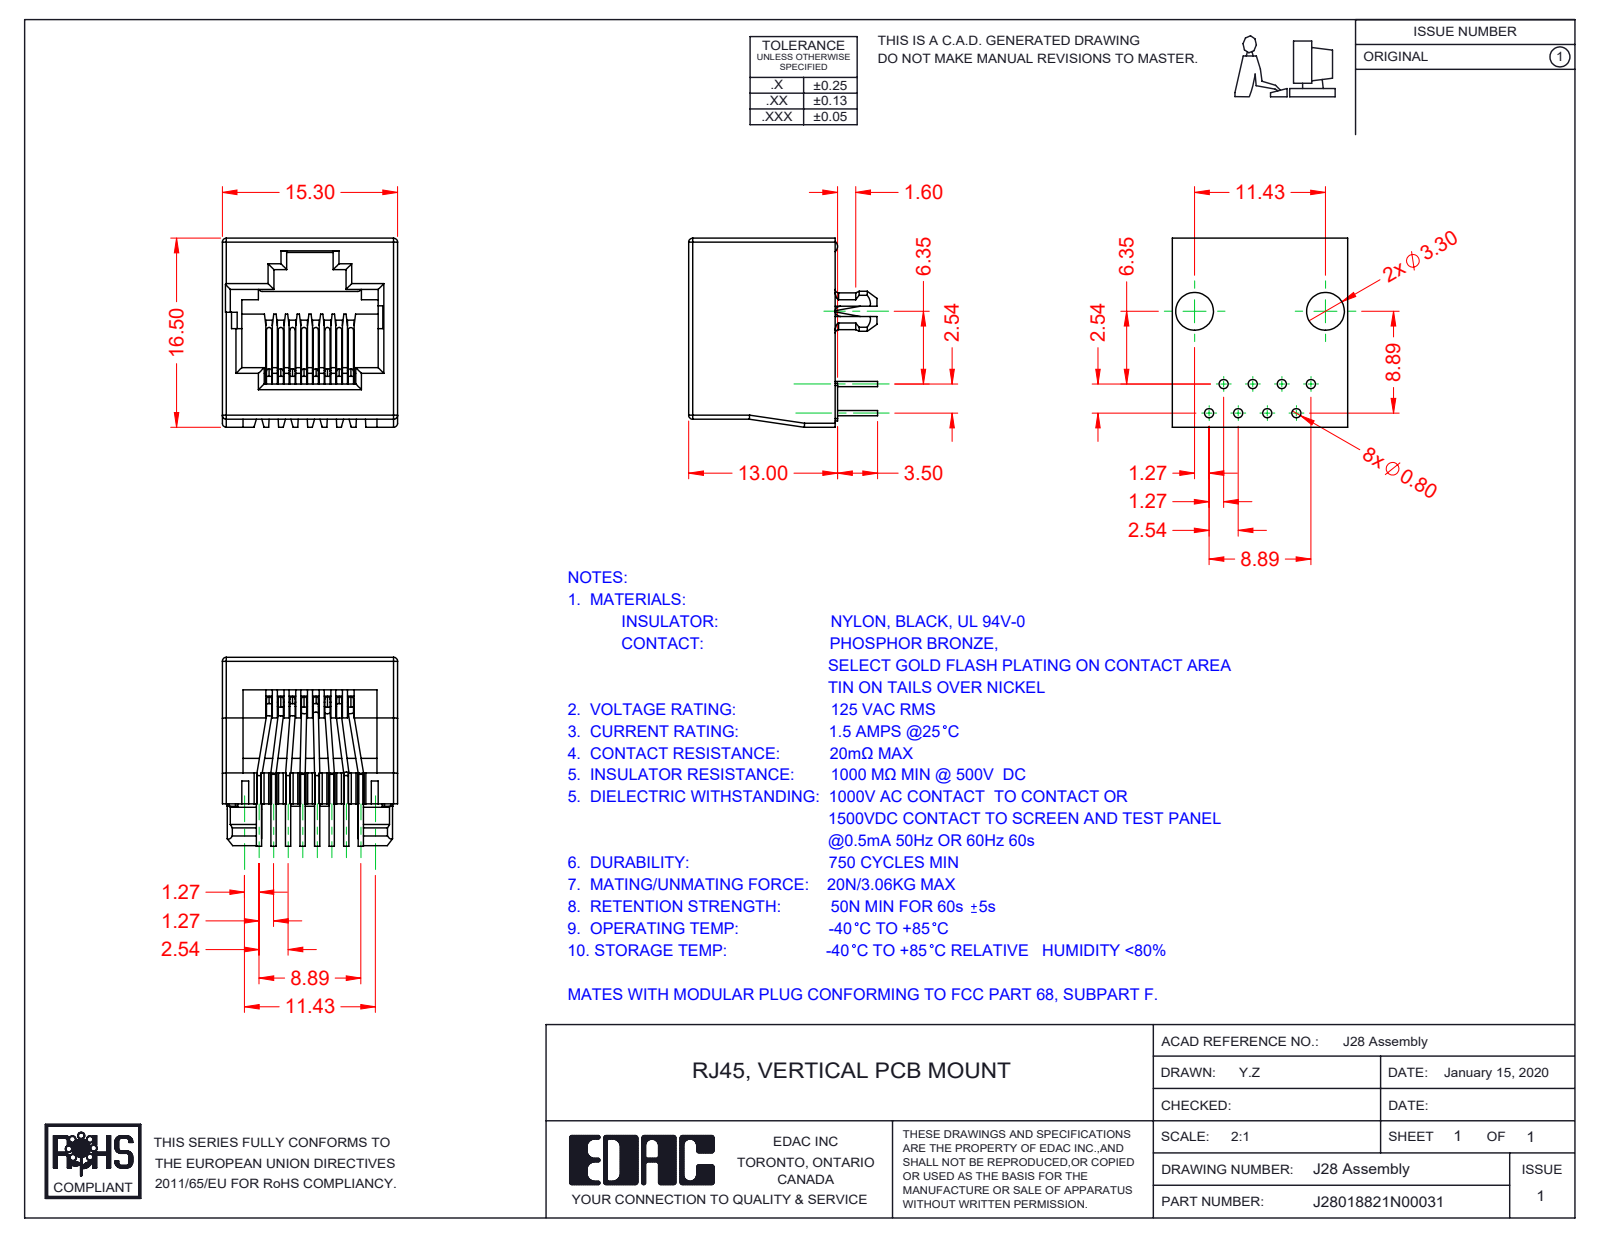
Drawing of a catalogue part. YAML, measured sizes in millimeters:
part_name: "RJ28018821N00031; 28 Contacts; 28 Insulator"
step_written_by: "SolidWorks 2016 (CONFIG_CONTROL_DESIGN)"
units: millimeters
bodies: {solids: 9, faces: 580, planar: 319, cylindrical: 205, other: 56}
overall_size: [16.5, 16.5, 15.3]
volume: 1535
surface_area: 2745
round_holes:
  - {diameter: 1.6, count: 2}
round_bosses_or_shafts:
  - {diameter: 0.46, count: 45}
partial_cylinders:
  - {radius: 0.5, count: 19}
  - {radius: 0.1, count: 16}
  - {radius: 0.35, count: 14}
  - {radius: 0.25, count: 10}
  - {radius: 0.2, count: 8}
  - {radius: 0.23, count: 8}
  - {radius: 0.45, count: 2}
  - {radius: 1.6, count: 2}
face_to_face_distances: [15.3, 1.02, 1.7, 13.6, 1.25, 2.04, 12.81, 3.06, 3.15, 12.15]
hole_center_spacings: [12]
